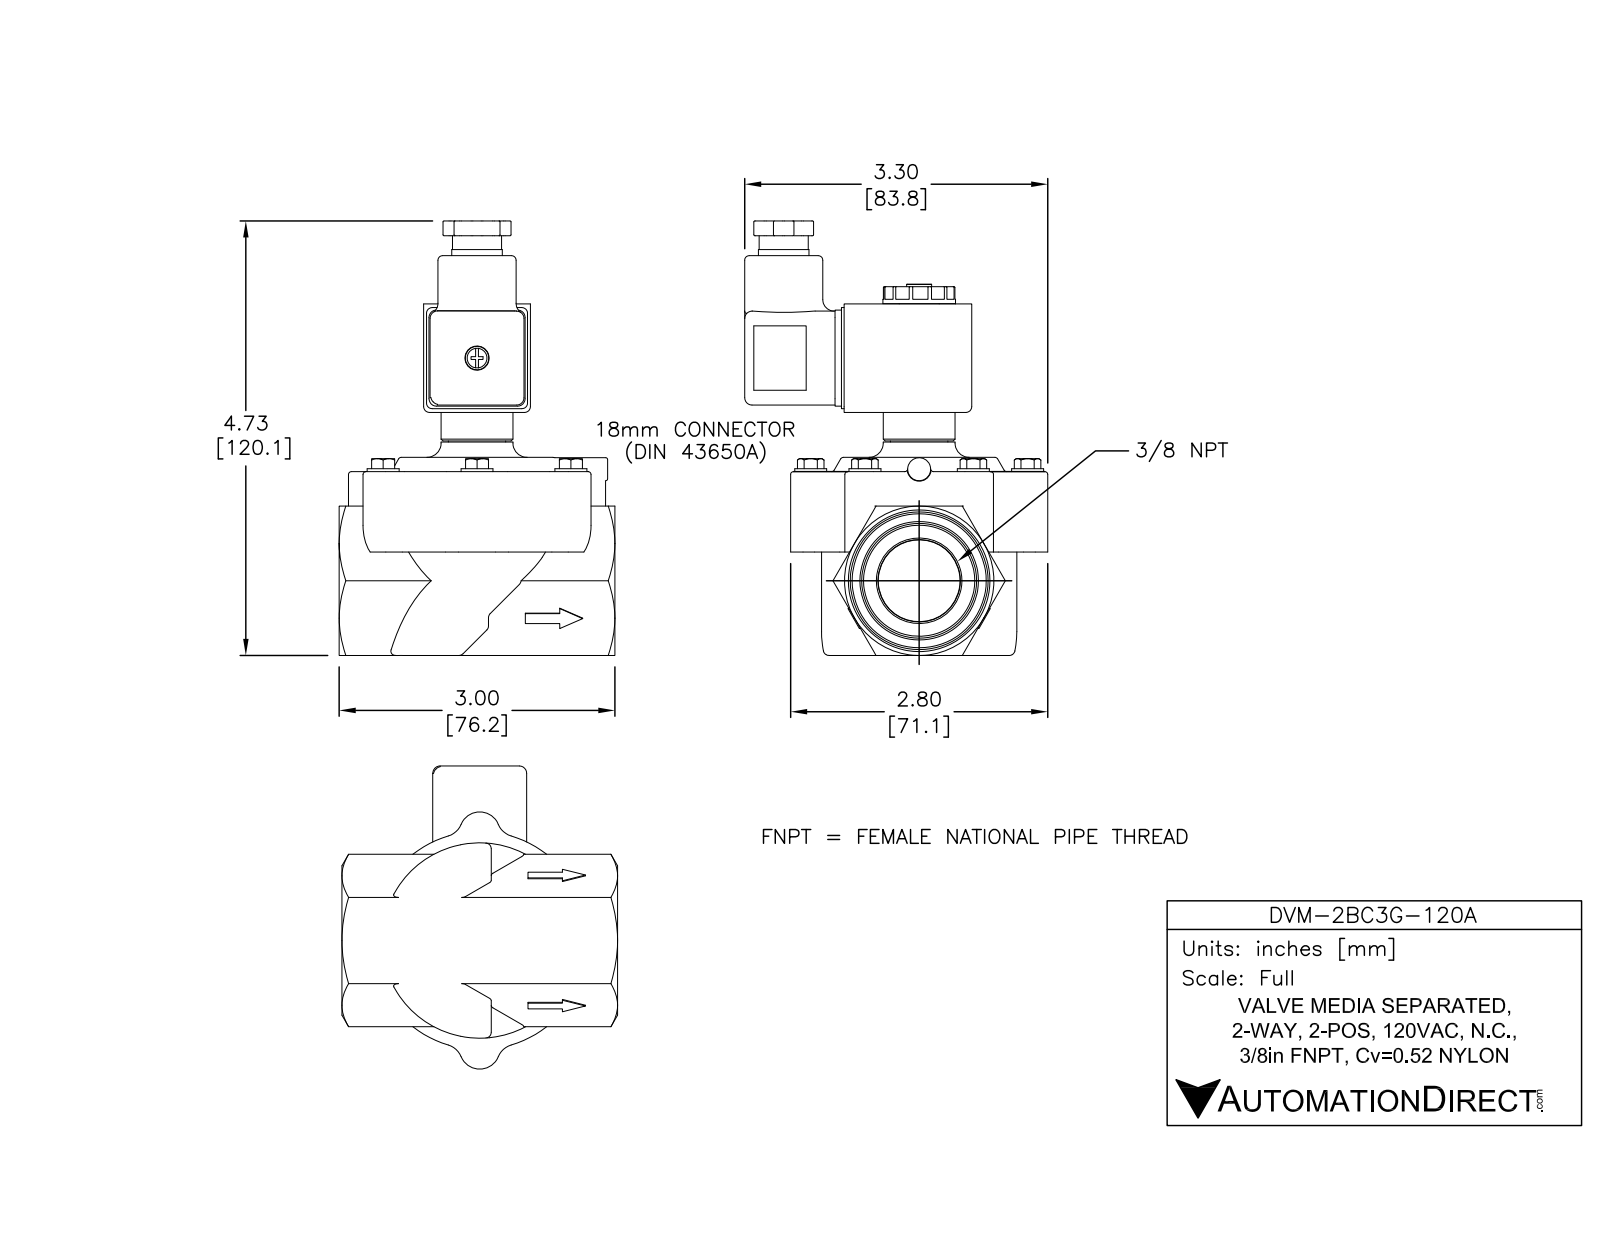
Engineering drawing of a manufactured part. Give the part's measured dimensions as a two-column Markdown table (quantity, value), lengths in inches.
| quantity | value |
| --- | --- |
| part name | DVD-2BC5F-24D |
| STEP written by | SolidWorks 2015 (AUTOMOTIVE_DESIGN) |
| units | inches |
| bodies | 4 solids, 1888 faces (891 planar, 379 cylindrical, 618 other) |
| overall size | 4.727 × 3.298 × 3 |
| volume | 9.098 in³ |
| surface area | 104.5 in² |
| round holes (diameter × count) | 0.2 × 6, 0.236 × 6, 0.185 × 4, 0.06 × 2, 0.062 × 2, 0.125 × 2, 0.156 × 2, 0.185 × 2, 0.047 × 1, 0.065 × 1, 0.078 × 1, 0.089 × 1 |
| round bosses / shafts (diameter × count) | 0.348 × 6, 0.234 × 6, 0.164 × 6, 1.844 × 1, 1.5 × 1, 1.359 × 1, 0.85 × 1, 0.79 × 1 |
| partial cylindrical surfaces (radius × count) | 0.01 × 48, 0.219 × 20, 0.062 × 12, 0.08 × 12, 0.156 × 12, 0.03 × 10, 0.05 × 8, 0.031 × 7 |
| main face-to-face distances | 1.615, 1.635, 0.125, 0.02, 0.92, 2.08, 1.625, 0.155, 0.25, 0.048 |
| hole center spacings | 1.18, 1.18, 2.044, 0.611, 1.669, 2.28, 1.103, 1.169 |
